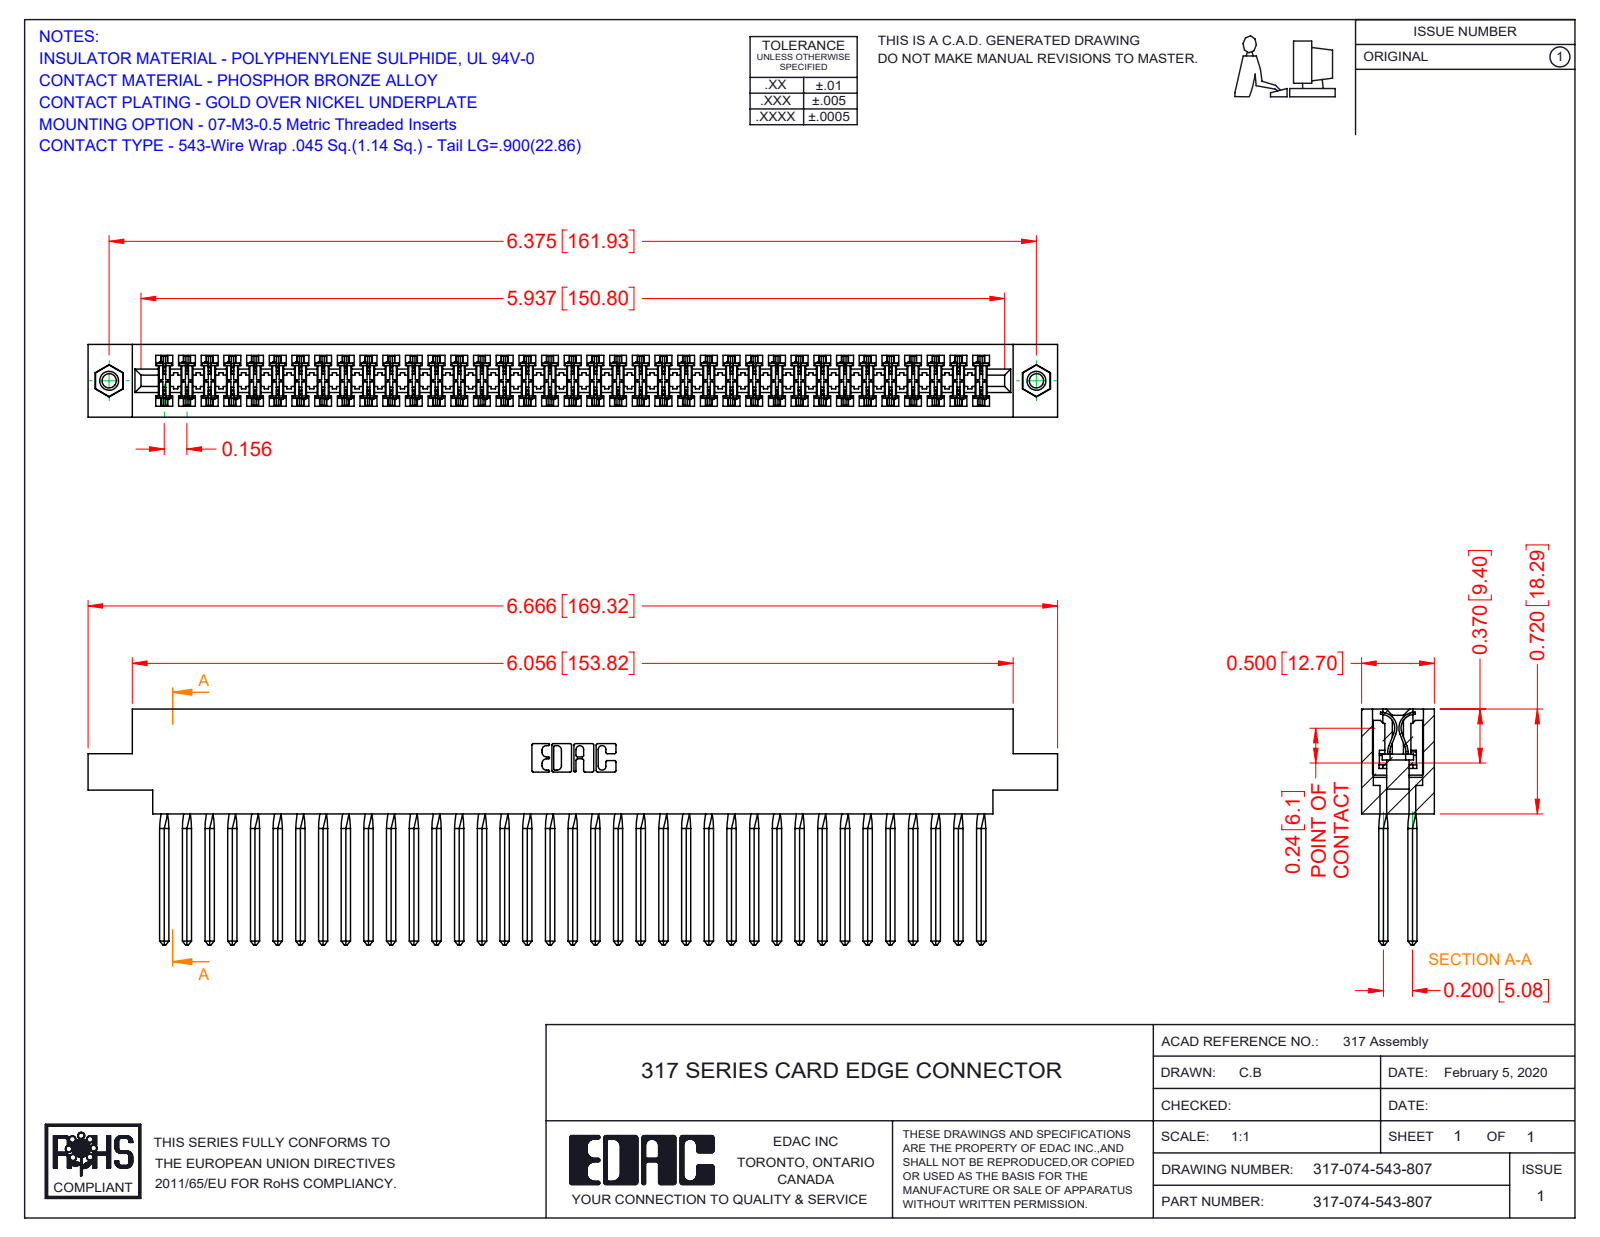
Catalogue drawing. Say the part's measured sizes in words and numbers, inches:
The part is named "317-074-543-807; 317-290-001_543; 317 Part_.156 Dia - TI; 345-250-001_345-250-005-103". Its 3-D file was written by "SolidWorks 2016 (CONFIG_CONTROL_DESIGN)". It is 77 solids with 6748 faces: 5492 planar, 944 cylindrical and 312 other. Overall it measures 6.666 by 1.62 by 0.5 inches. Its volume is 1.745 cubic inches and its surface area 67.01 square inches. Round holes: 2 of diameter 0.098, 2 of diameter 0.125, 2 of diameter 0.156. Round bosses or shafts: 2 of diameter 0.155. Partial cylindrical surfaces (rounded edges, fillets, slot ends): 148 of radius 0.015, 22 of radius 0.01, 6 of radius 0.007, 6 of radius 0.031, 3 of radius 0.026, 2 of radius 0.095, 2 of radius 0.1, 2 of radius 0.11. The main face-to-face distances are 0.5, 0.075, 0.425, 0.35, 0.11, 0.195, 0.094, 0.2, 0.115, 0.131. The hole center spacings are 6.375.
